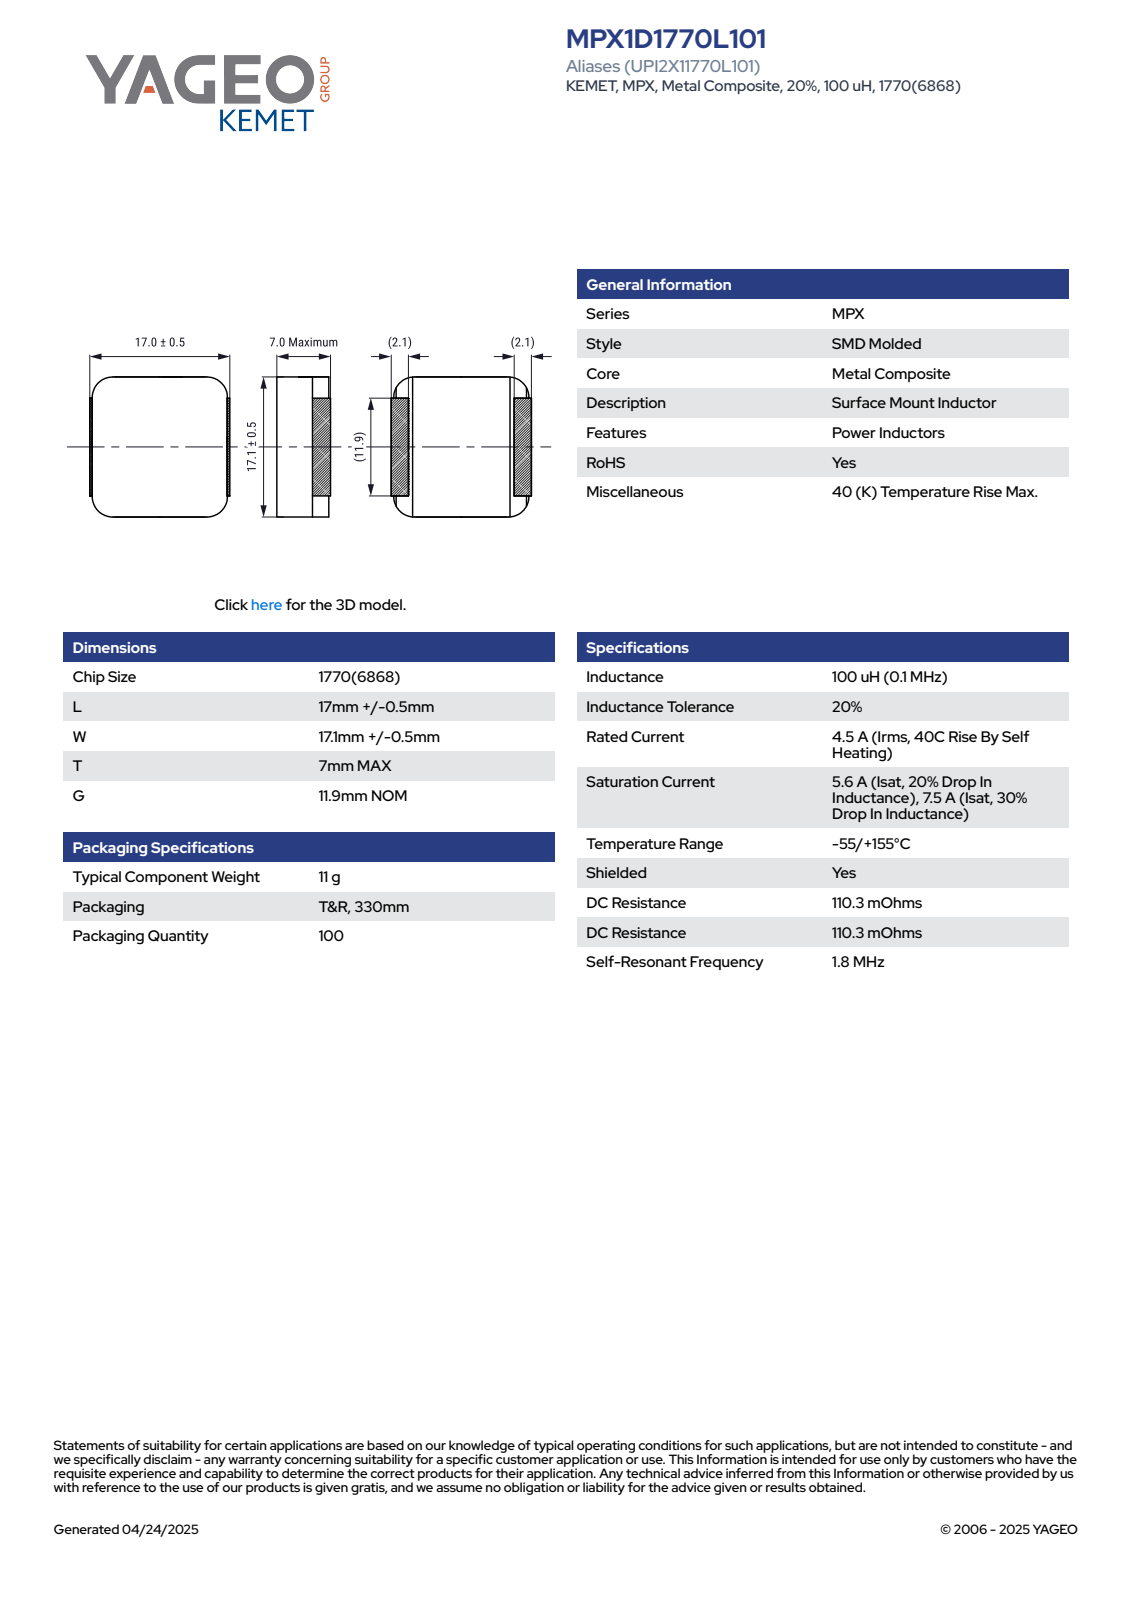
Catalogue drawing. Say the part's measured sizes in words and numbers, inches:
The part is named "MPX1D1770(KEMET)". Its 3-D file was written by "SolidWorks 2018 (AUTOMOTIVE_DESIGN)". It is 1 solid with 122 faces: 104 planar, 18 cylindrical and 0 other. Overall it measures 0.693 by 0.689 by 0.276 inches. Its volume is 0.12 cubic inches and its surface area 1.77 square inches. Partial cylindrical surfaces (rounded edges, fillets, slot ends): 4 of radius 0.012, 4 of radius 0.098, 4 of radius 0.098. The main face-to-face distances are 0.272, 0.693, 0.02, 0.657, 0.65, 0.264, 0.638, 0.276, 0.031, 0.669.
